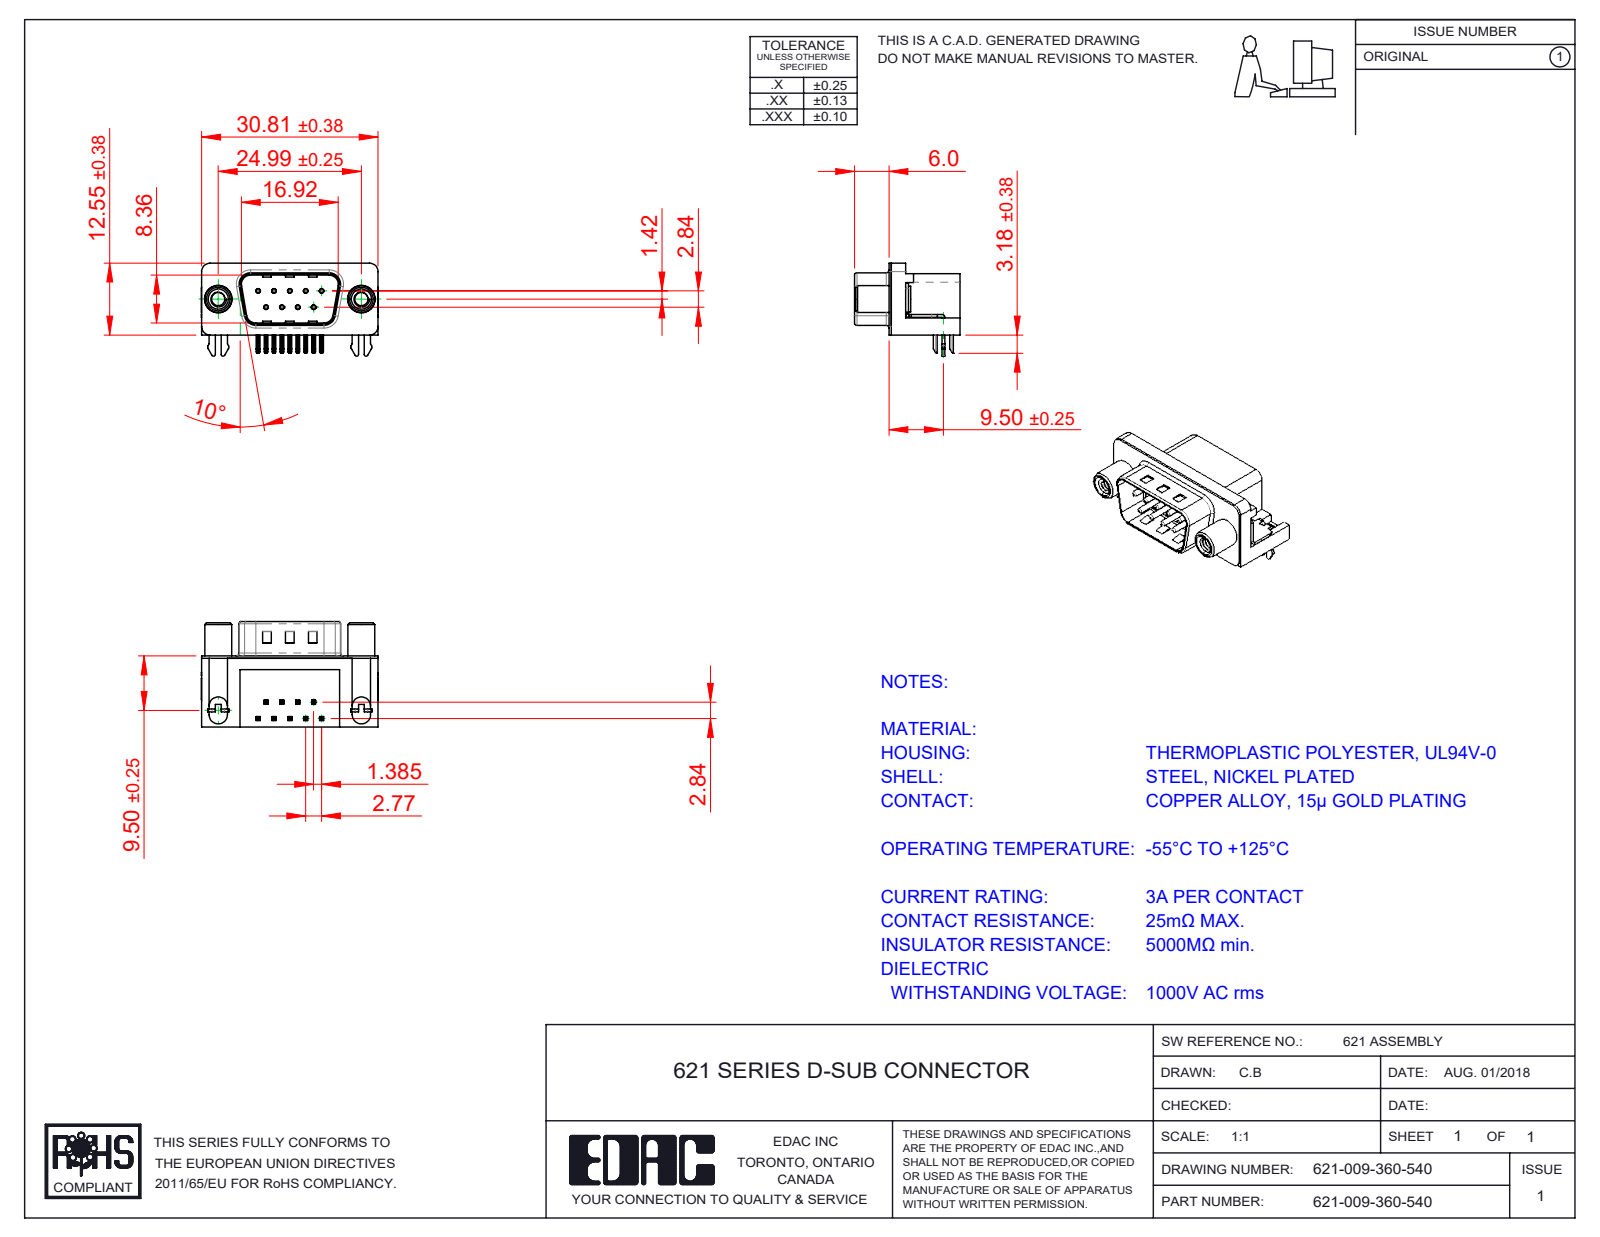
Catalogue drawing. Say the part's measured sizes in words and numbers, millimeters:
The part is named "621 Housing_9 Socket; 621 Shell_9 Socket; 621 Contact Bottom; 621 4 Prong Board Lock (+3 more)". Its 3-D file was written by "SolidWorks 2016 (CONFIG_CONTROL_DESIGN)". It is 15 solids with 1105 faces: 607 planar, 329 cylindrical and 169 other. Overall it measures 30.89 by 18.4 by 16.25 millimeters. Its volume is 3 346 cubic millimeters and its surface area 4 695 square millimeters. Round holes: 9 of diameter 0.35, 9 of diameter 0.8, 2 of diameter 2, 2 of diameter 2.3, 2 of diameter 3.1, 2 of diameter 4, 2 of diameter 4.8, 2 of diameter 5. Round bosses or shafts: 9 of diameter 0.75, 2 of diameter 4.9, 2 of diameter 4.7, 2 of diameter 4.5, 2 of diameter 3.85, 2 of diameter 3. Partial cylindrical surfaces (rounded edges, fillets, slot ends): 40 of radius 0.25, 18 of radius 0.12, 16 of radius 1, 9 of radius 0.5, 8 of radius 1.5, 8 of radius 1.6, 4 of radius 0.9, 4 of radius 2. The main face-to-face distances are 0.4, 12, 12.4, 10.35, 9.5, 2.5, 2.9, 2.1, 0.35, 10.7. The hole center spacings are 3.16, 2.77, 5.54, 5.03, 5.04, 8.31, 7.48, 7.49.
